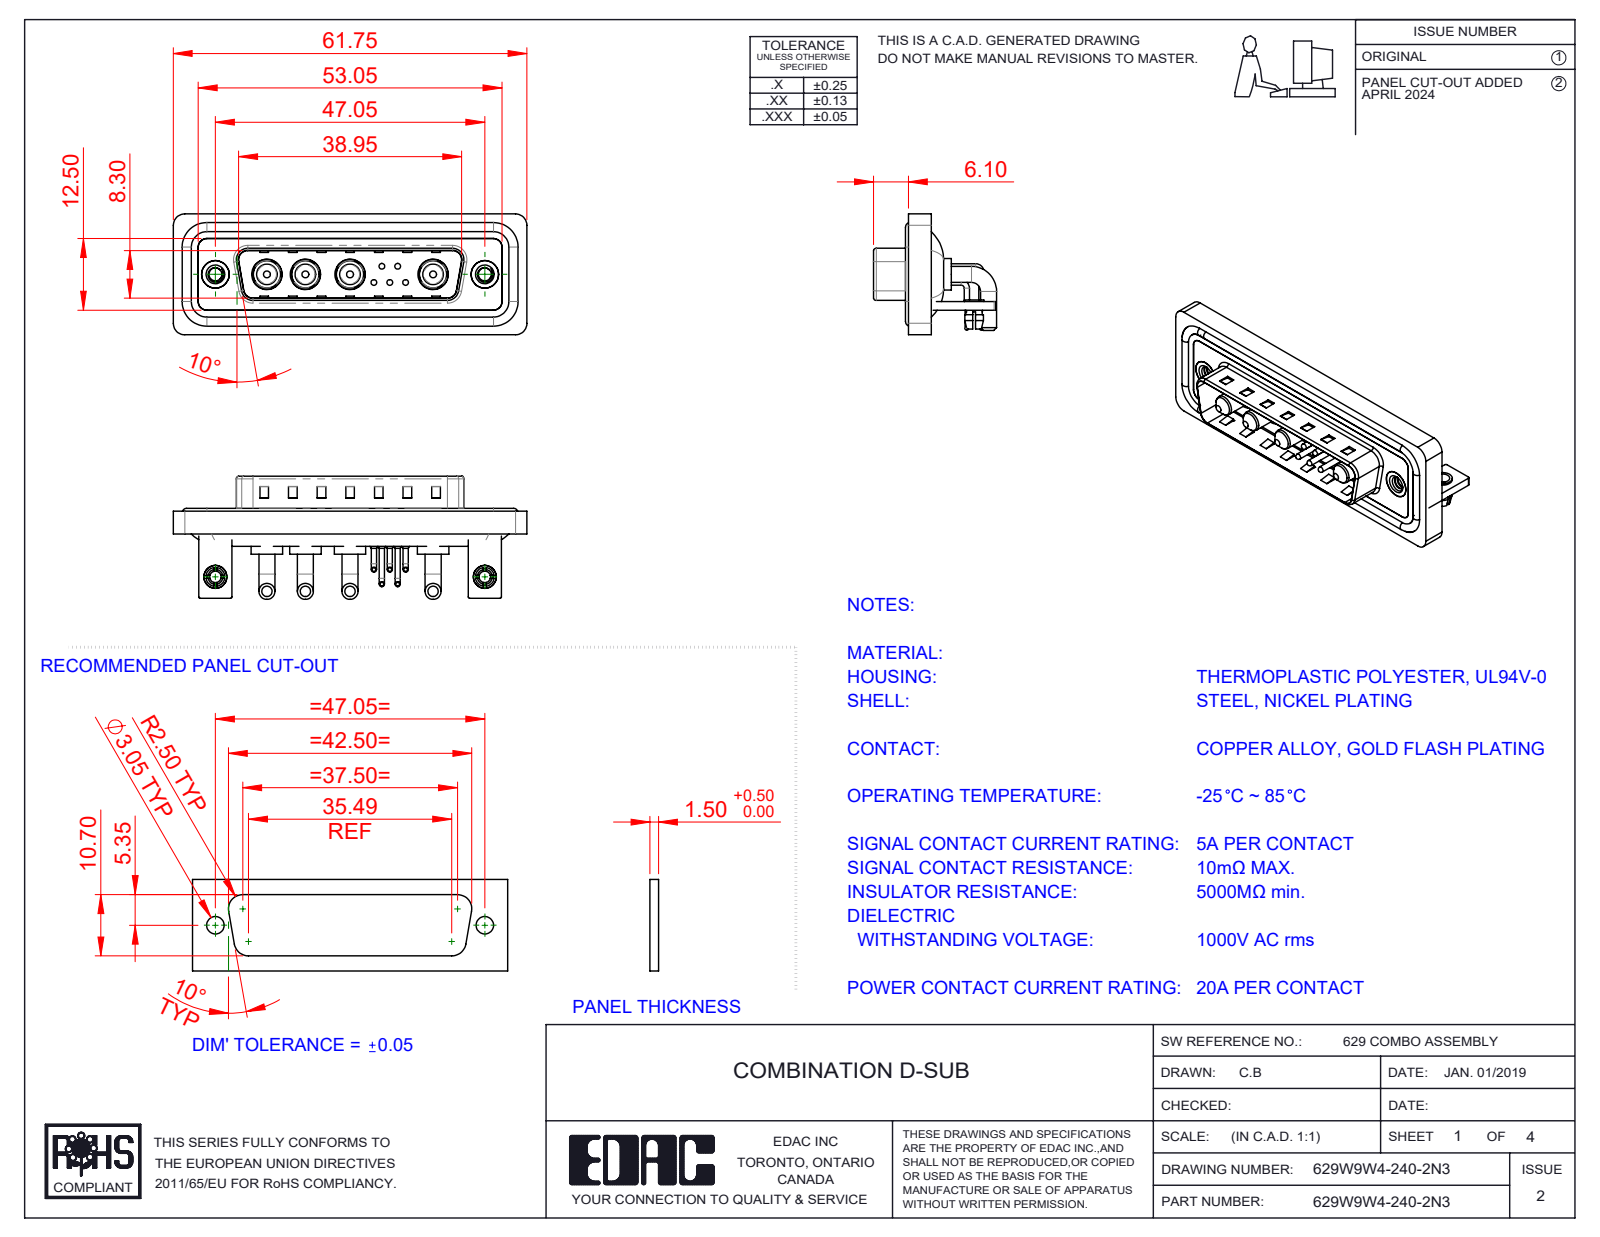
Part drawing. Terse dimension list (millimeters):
name: 629Combo Waterproof Housing_25 Contacts; 629Combo Shell Rear_25 Contacts; 629Combo Stabilizer Bracket; 629Combo Board Lock (+7 more)
written by: SolidWorks 2023 (CONFIG_CONTROL_DESIGN)
unit: mm
bodies: 24 solids, 1337 faces (637 planar, 502 cylindrical, 198 other)
size: 61.75 × 21.5 × 21.1
volume: 8 018 mm³; area: 13 174 mm²
holes: 7× ⌀2, 5× ⌀0.75, 5× ⌀1.6, 4× ⌀4.85, 4× ⌀5.3, 2× ⌀2.26, 2× ⌀2.5, 2× ⌀3.2, 2× ⌀4, 2× ⌀4.8, 2× ⌀5
bosses: 10× ⌀0.9, 8× ⌀2.8, 5× ⌀1.5, 5× ⌀1, 5× ⌀0.65, 4× ⌀5.5, 4× ⌀5.2, 4× ⌀4.75
rounds: 19× R2, 18× R1.5, 16× R0.25, 9× R0.5, 8× R1.6, 5× R1.01, 4× R0.6, 4× R0.65
face distances: 0.4, 1.5, 0.8, 2.9, 2.1, 1.1, 3.7, 4.1, 4.5, 1.6
hole spacings: 3.16, 2.77, 5.04, 14.5, 47.05, 2.78, 4.4, 4.41
